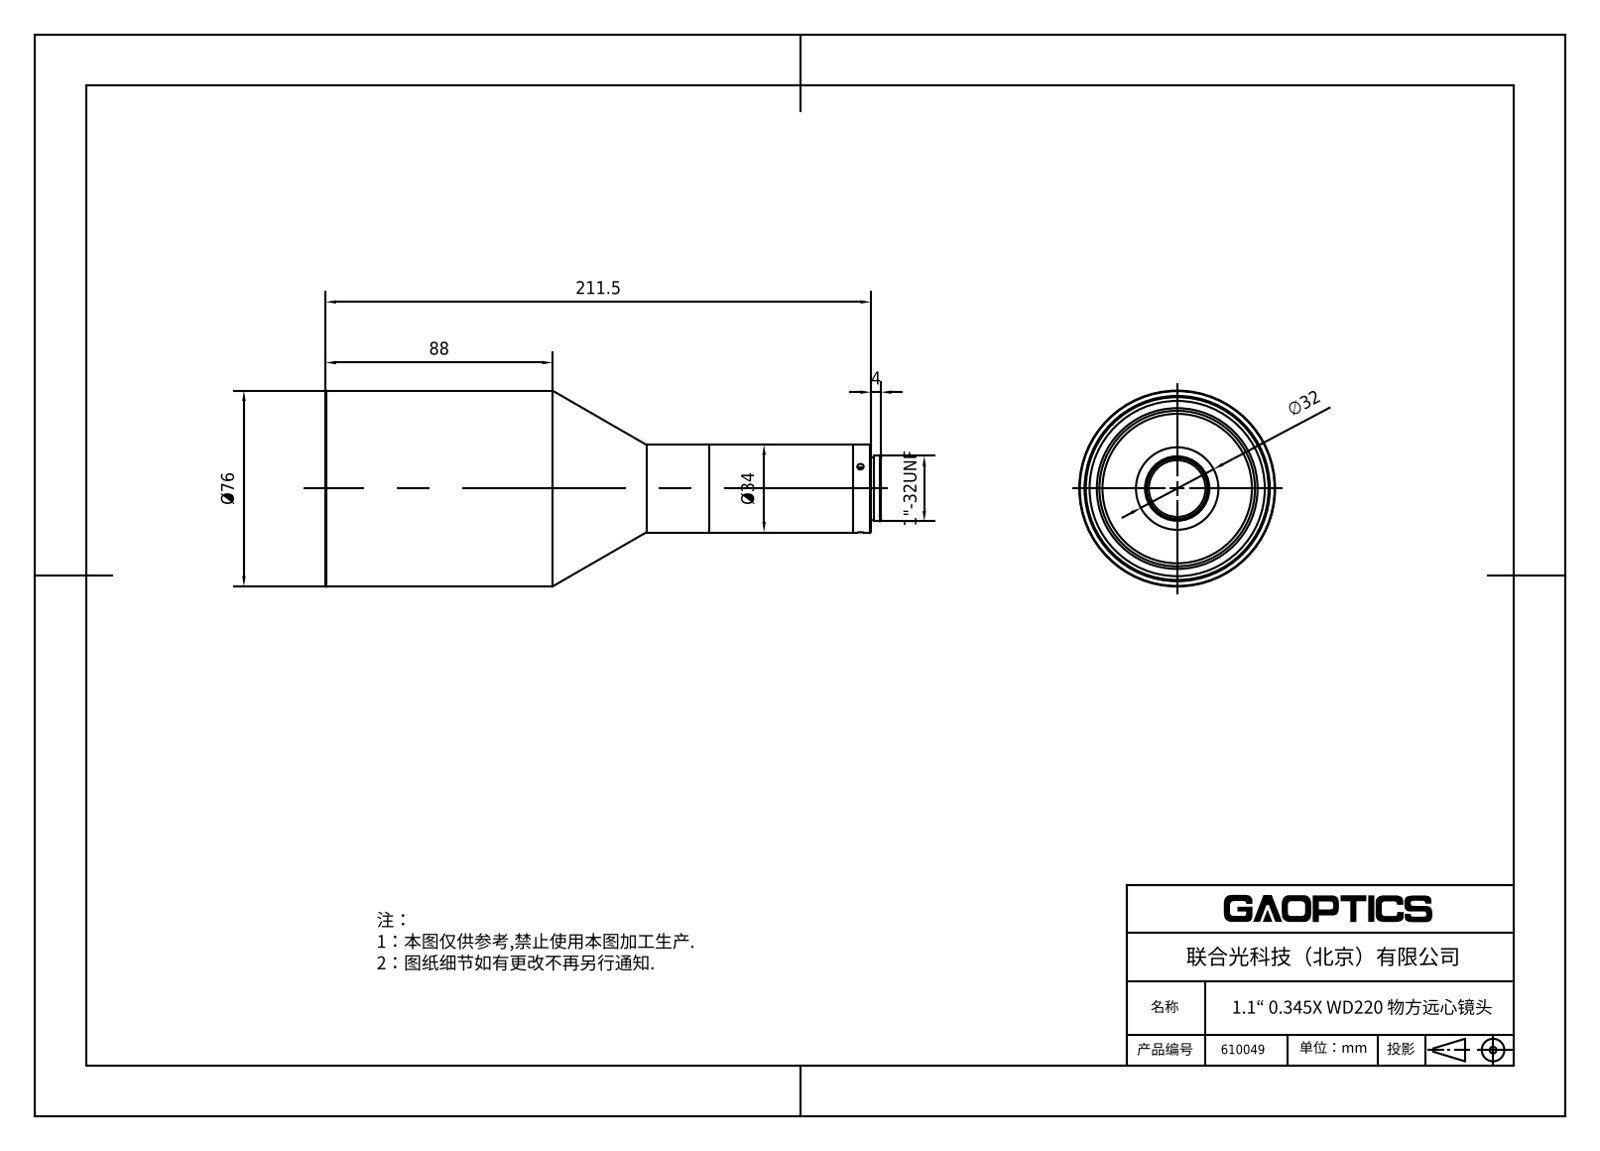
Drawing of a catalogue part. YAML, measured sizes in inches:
part_name: "610049"
step_written_by: "SolidWorks 2020 (CONFIG_CONTROL_DESIGN)"
units: inches
bodies: {solids: 2, faces: 80, planar: 17, cylindrical: 41, other: 22}
overall_size: [8.485, 2.992, 2.992]
volume: 30.37
surface_area: 79.48
round_holes:
  - {diameter: 0.097, count: 2}
  - {diameter: 0.097, count: 1}
  - {diameter: 0.866, count: 1}
  - {diameter: 0.961, count: 1}
  - {diameter: 0.973, count: 1}
  - {diameter: 0.992, count: 1}
  - {diameter: 2.677, count: 1}
  - {diameter: 2.792, count: 1}
  - {diameter: 2.843, count: 1}
round_bosses_or_shafts:
  - {diameter: 2.992, count: 1}
  - {diameter: 1.339, count: 1}
  - {diameter: 1.118, count: 1}
  - {diameter: 1.063, count: 1}
  - {diameter: 1, count: 1}
partial_cylinders:
  - {radius: 0.594, count: 1}
  - {radius: 0.596, count: 1}
face_to_face_distances: [7.412, 6.849, 0.563, 0.345, 7.194, 7.757, 0.217, 0.295, 0.641, 7.49]
